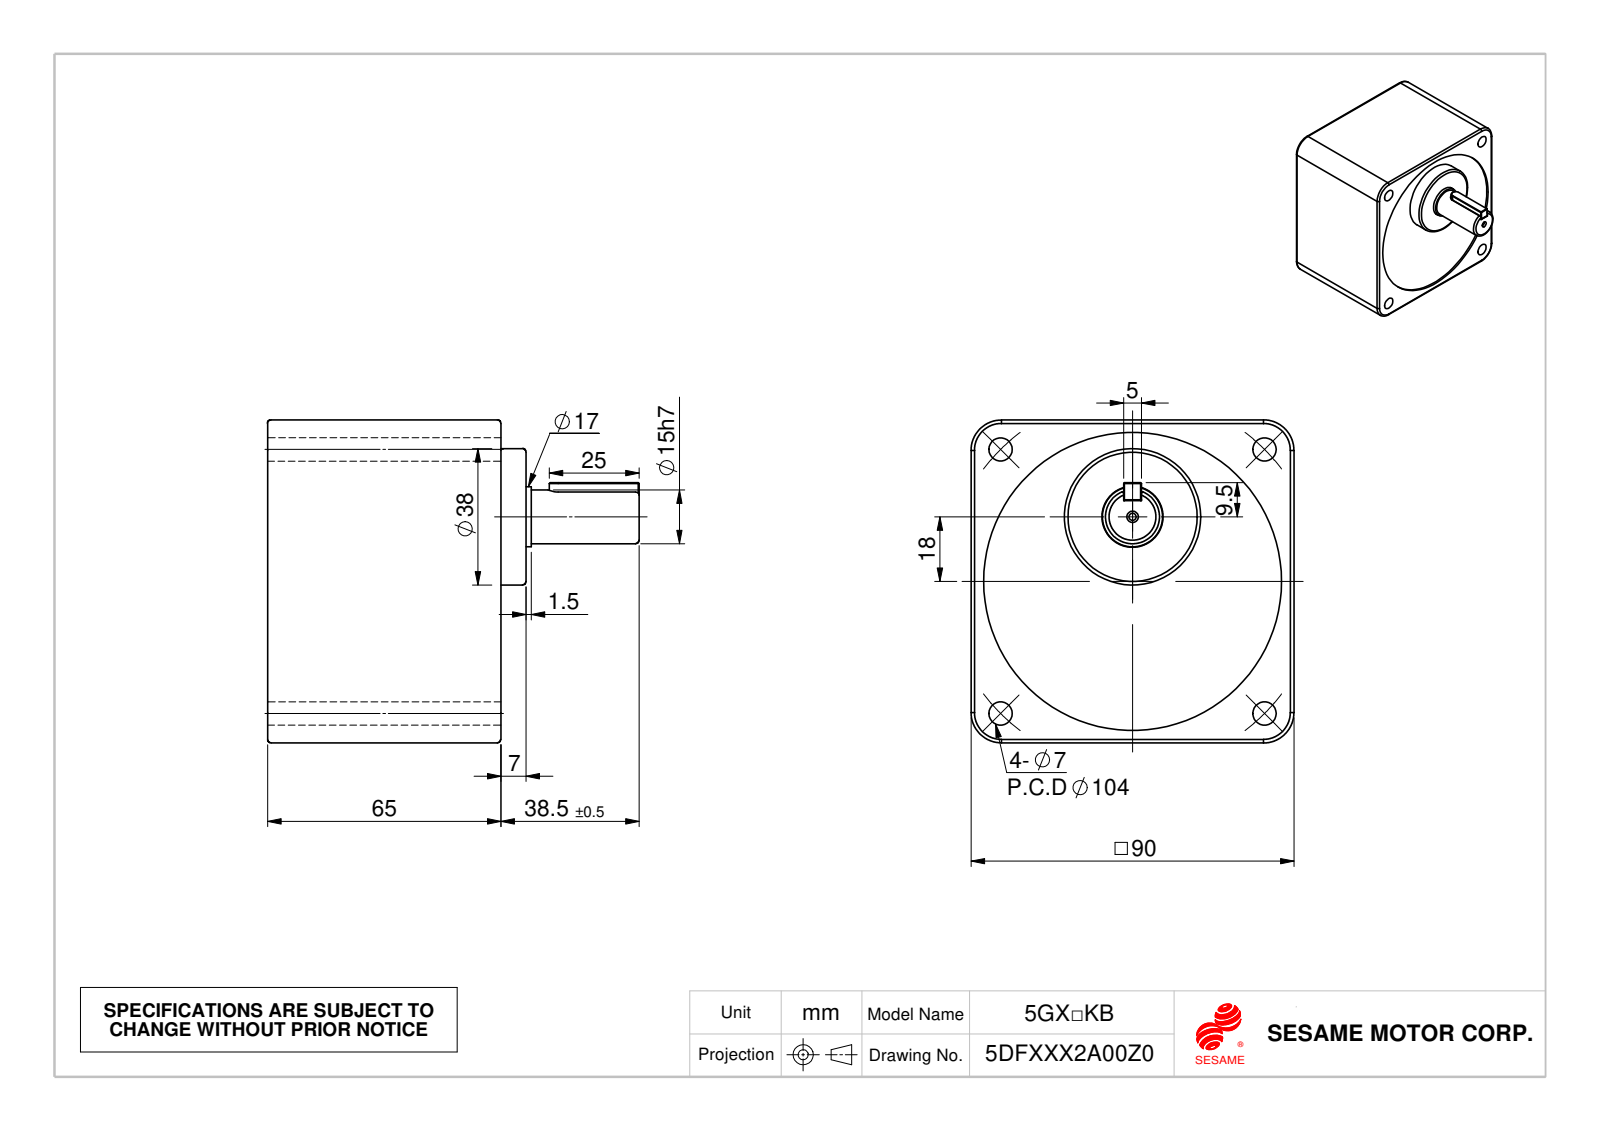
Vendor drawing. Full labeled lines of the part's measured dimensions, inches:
Part name (STEP PRODUCT): 側板成品(簡易); 1715-2A_5.成品; 5x5xL_25L
STEP written by: SolidWorks 2010 (CONFIG_CONTROL_DESIGN)
Units: inches
Bodies: 4 solids, 99 faces (38 planar, 43 cylindrical, 18 other)
Overall size (bounding box): 4.075 × 3.543 × 3.543
Volume: 30.61 in³ · Surface area: 95.97 in²
Round holes (diameter × count): ⌀0.256 ×4, ⌀0.079 ×1, ⌀0.48 ×1, ⌀0.669 ×1, ⌀3.267 ×1, ⌀3.268 ×1
Round bosses / shafts (diameter × count): ⌀3.26 ×1, ⌀2.756 ×1, ⌀1.496 ×1, ⌀0.657 ×1, ⌀0.591 ×1
Partial cylindrical surfaces — rounded edges, fillets, slot ends (radius × count): R0.039 ×8, R0.335 ×4, R0.098 ×1
Main face-to-face distances: 3.543, 2.165, 0.22, 2.386, 0.134, 0.354, 2.52, 2.559, 2.425, 2.205
Hole centre spacings: 2.047, 2.895, 1.625, 2.597, 4.094, 0.709
